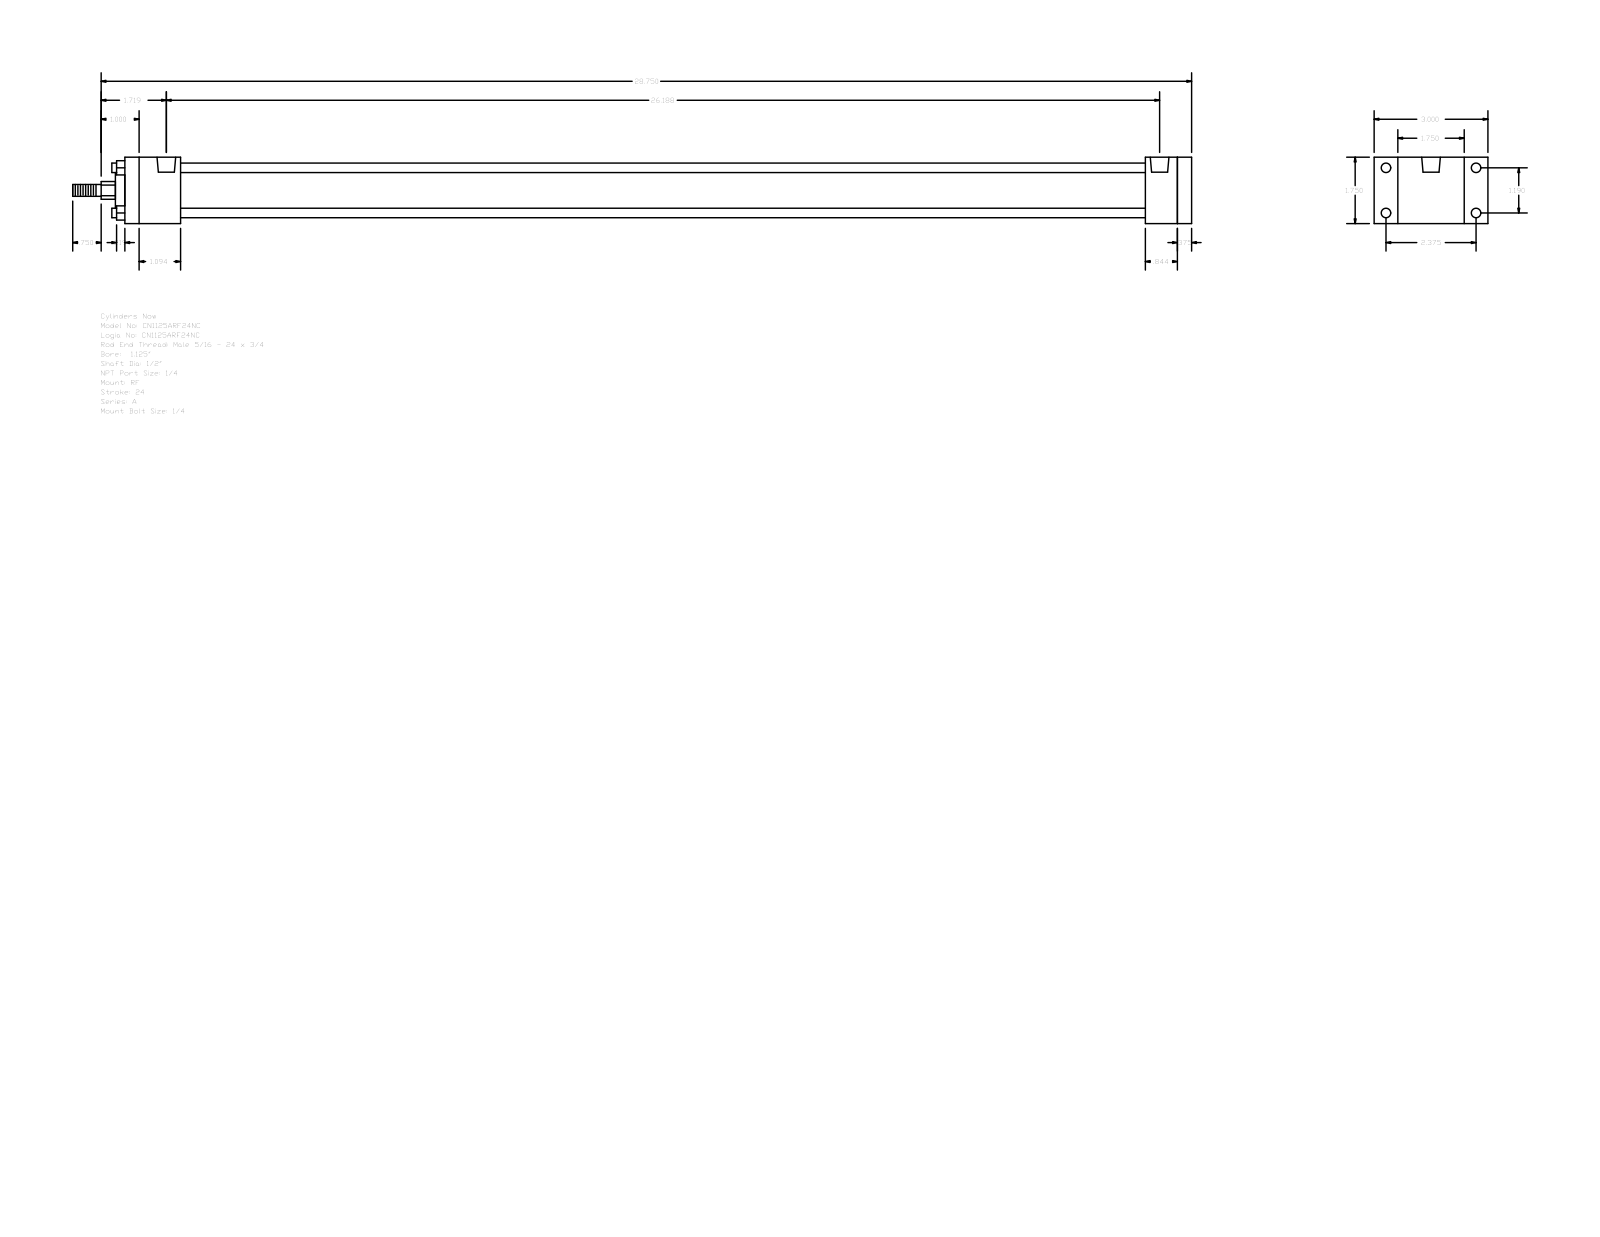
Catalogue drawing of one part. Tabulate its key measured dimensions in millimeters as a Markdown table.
| quantity | value |
| --- | --- |
| part name | A_RF__0112_0.5 |
| STEP written by | GSSL Pune (CONFIG_CONTROL_DESIGN) |
| units | millimeters |
| bodies | 0 solids, 92 faces (64 planar, 28 cylindrical, 0 other) |
| overall size | 749.3 × 76.2 × 44.45 |
| round holes (diameter × count) | 5.56 × 4, 6.35 × 4, 12.49 × 2 |
| round bosses / shafts (diameter × count) | 6.35 × 4, 31.88 × 1, 23.81 × 1, 12.7 × 1, 7.94 × 1 |
| partial cylindrical surfaces (radius × count) | 5.94 × 1 |
| main face-to-face distances | 44.46, 9.52, 704.85, 714.37, 37.3, 683.41, 646.11, 667.55, 677.07, 21.44 |
| hole center spacings | 30.22, 60.32, 67.47, 661.99, 1.58, 1.59, 663.57, 663.58 |
